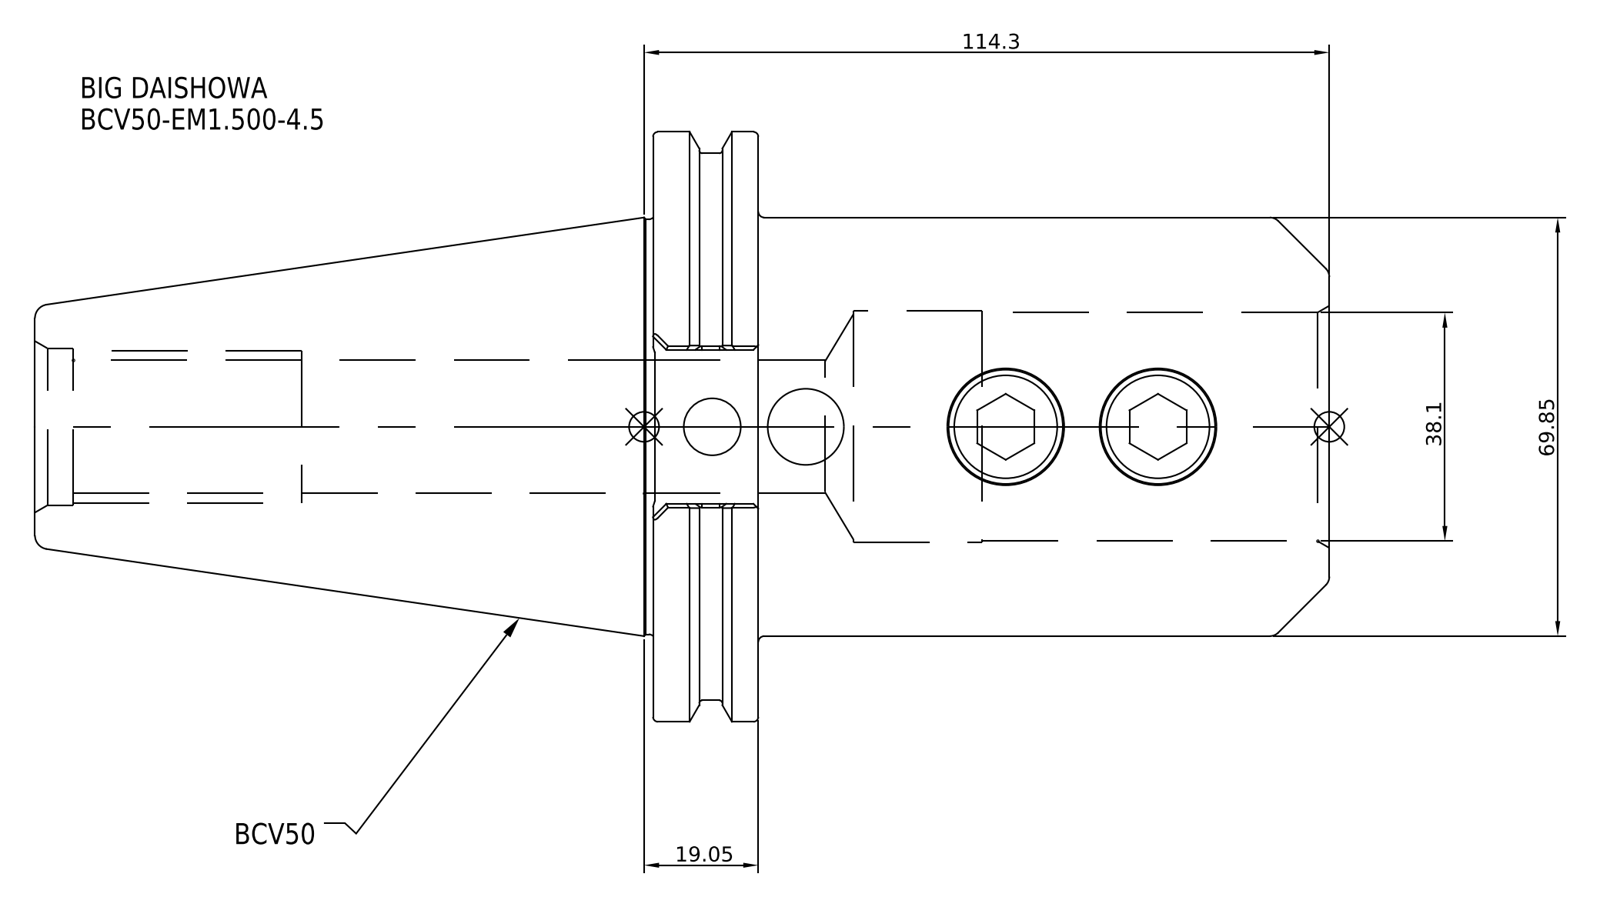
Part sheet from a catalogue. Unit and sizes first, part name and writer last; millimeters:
Units: millimetres
Overall size (bounding box): 215.9 × 98.43 × 98.43
Round holes (diameter × count): ⌀38.1 ×1
Round bosses / shafts (diameter × count): ⌀98.43 ×1, ⌀91.29 ×1, ⌀69.85 ×1
Main face-to-face distances: 17.55, 120.65, 103.1, 16, 33.55, 136.65, 79.25, 95.25, 112.8, 215.9
Volume: 647 707 mm³ · Surface area: 66 583 mm²
Bodies: 1 solid, 27 faces (7 planar, 12 cylindrical, 8 other)
Part name (STEP PRODUCT): BCV50-EM1_500-4_5
STEP written by: SolidWorks 2021 (CONFIG_CONTROL_DESIGN)
